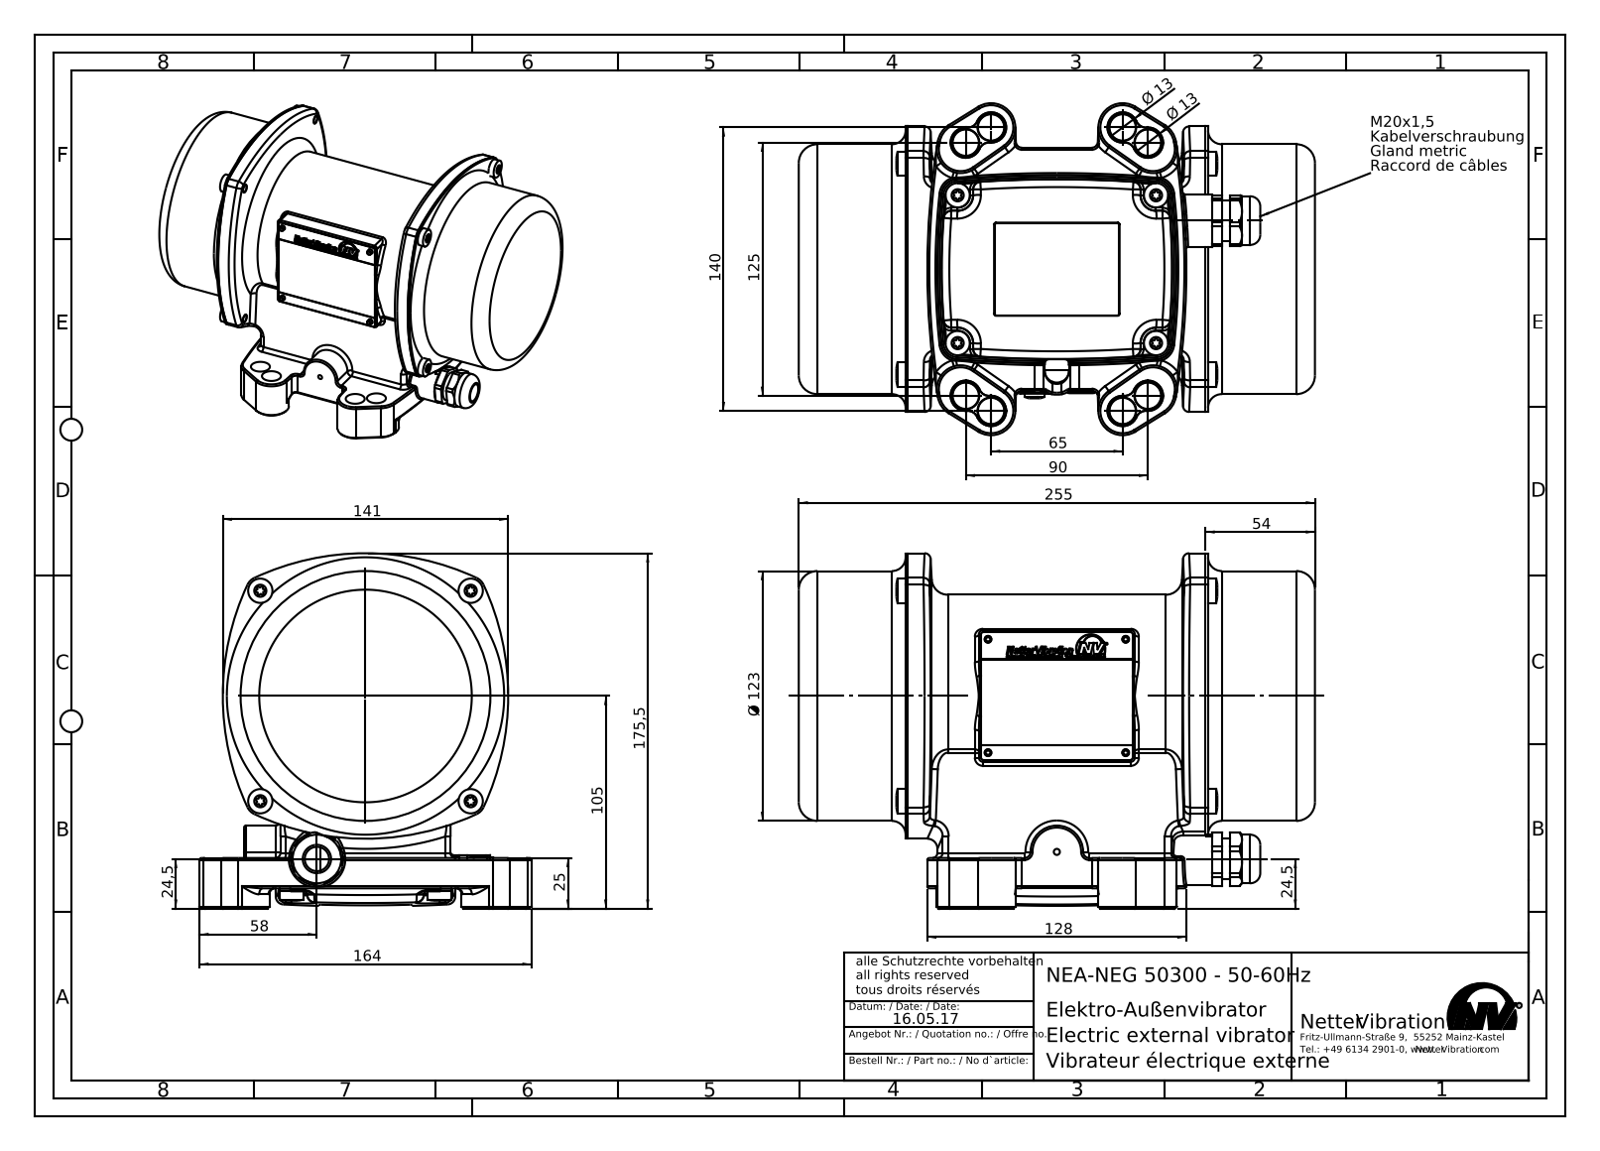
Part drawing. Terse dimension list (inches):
name: NEA-NEG 50300-50-60Hz
written by: SolidWorks 2015 (AUTOMOTIVE_DESIGN)
unit: in
bodies: 19 solids, 2652 faces (746 planar, 641 cylindrical, 1265 other)
size: 10.039 × 6.909 × 6.457
volume: 57.28 in³; area: 636.9 in²
holes: 4× ⌀0.134, 4× ⌀0.276, 1× ⌀0.413, 1× ⌀0.453, 1× ⌀0.472, 1× ⌀0.512, 1× ⌀0.571, 1× ⌀0.728, 1× ⌀4.134, 1× ⌀4.764
bosses: 8× ⌀0.472, 8× ⌀0.236, 1× ⌀4.858, 1× ⌀3.937, 1× ⌀1.024, 1× ⌀0.945, 1× ⌀0.787, 1× ⌀0.492
rounds: 49× R0.039, 44× R0.059, 42× R0.008, 40× R0.02, 27× R0.118, 12× R0.079, 9× R0.069, 9× R0.089
face distances: 0.047, 9.992, 7.913, 2.079, 2.126, 7.866, 10.039, 9.945, 0.335, 0.394
hole spacings: 2.894, 4.092, 2.205, 2.677, 3.468, 5.787, 0.913, 1.573
